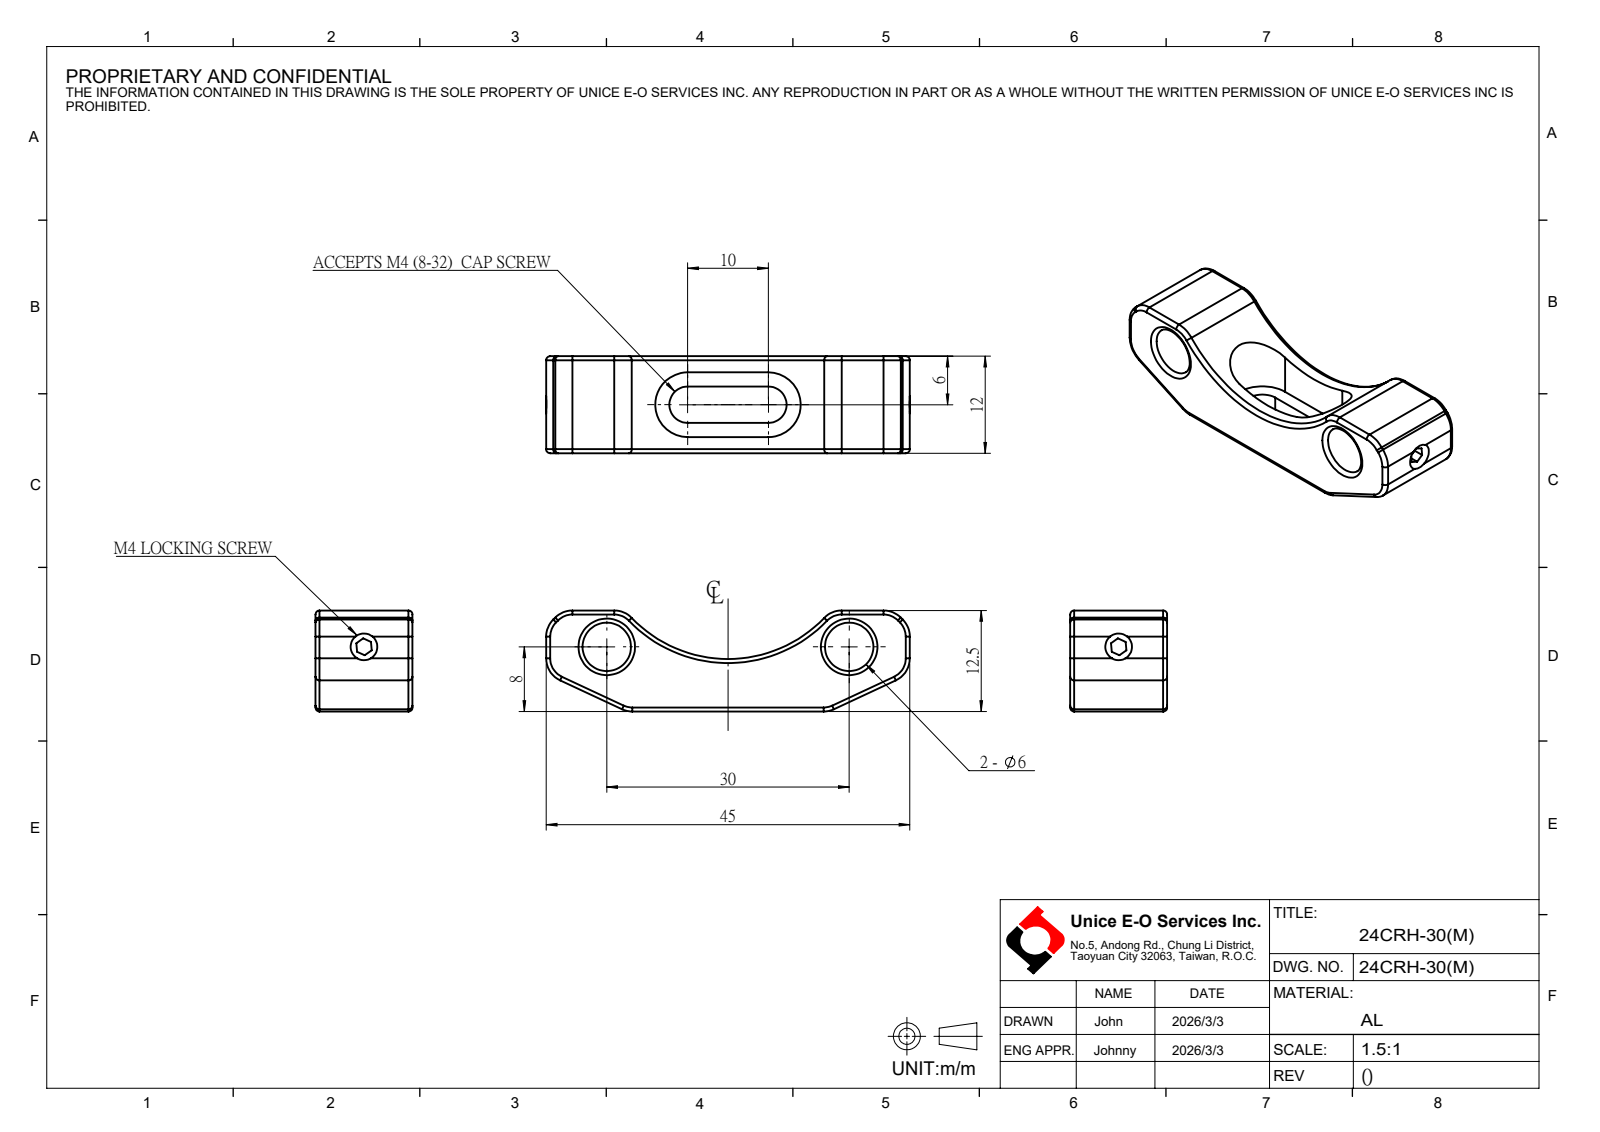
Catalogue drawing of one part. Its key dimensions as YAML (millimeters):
part_name: "24CRH-30(M)"
step_written_by: "SolidWorks 2024 (CONFIG_CONTROL_DESIGN)"
units: millimeters
bodies: {solids: 3, faces: 119, planar: 36, cylindrical: 45, other: 38}
overall_size: [45, 12.5, 12]
volume: 3356
surface_area: 2795
round_holes:
  - {diameter: 6, count: 2}
  - {diameter: 3.3, count: 1}
round_bosses_or_shafts:
  - {diameter: 4, count: 1}
partial_cylinders:
  - {radius: 0.5, count: 16}
  - {radius: 3, count: 10}
  - {radius: 2.25, count: 2}
  - {radius: 4, count: 2}
  - {radius: 16.5, count: 1}
face_to_face_distances: [12, 12.5, 2, 10, 2.1, 10.4, 8, 3.75, 8.25, 1.75]
hole_center_spacings: [30]
